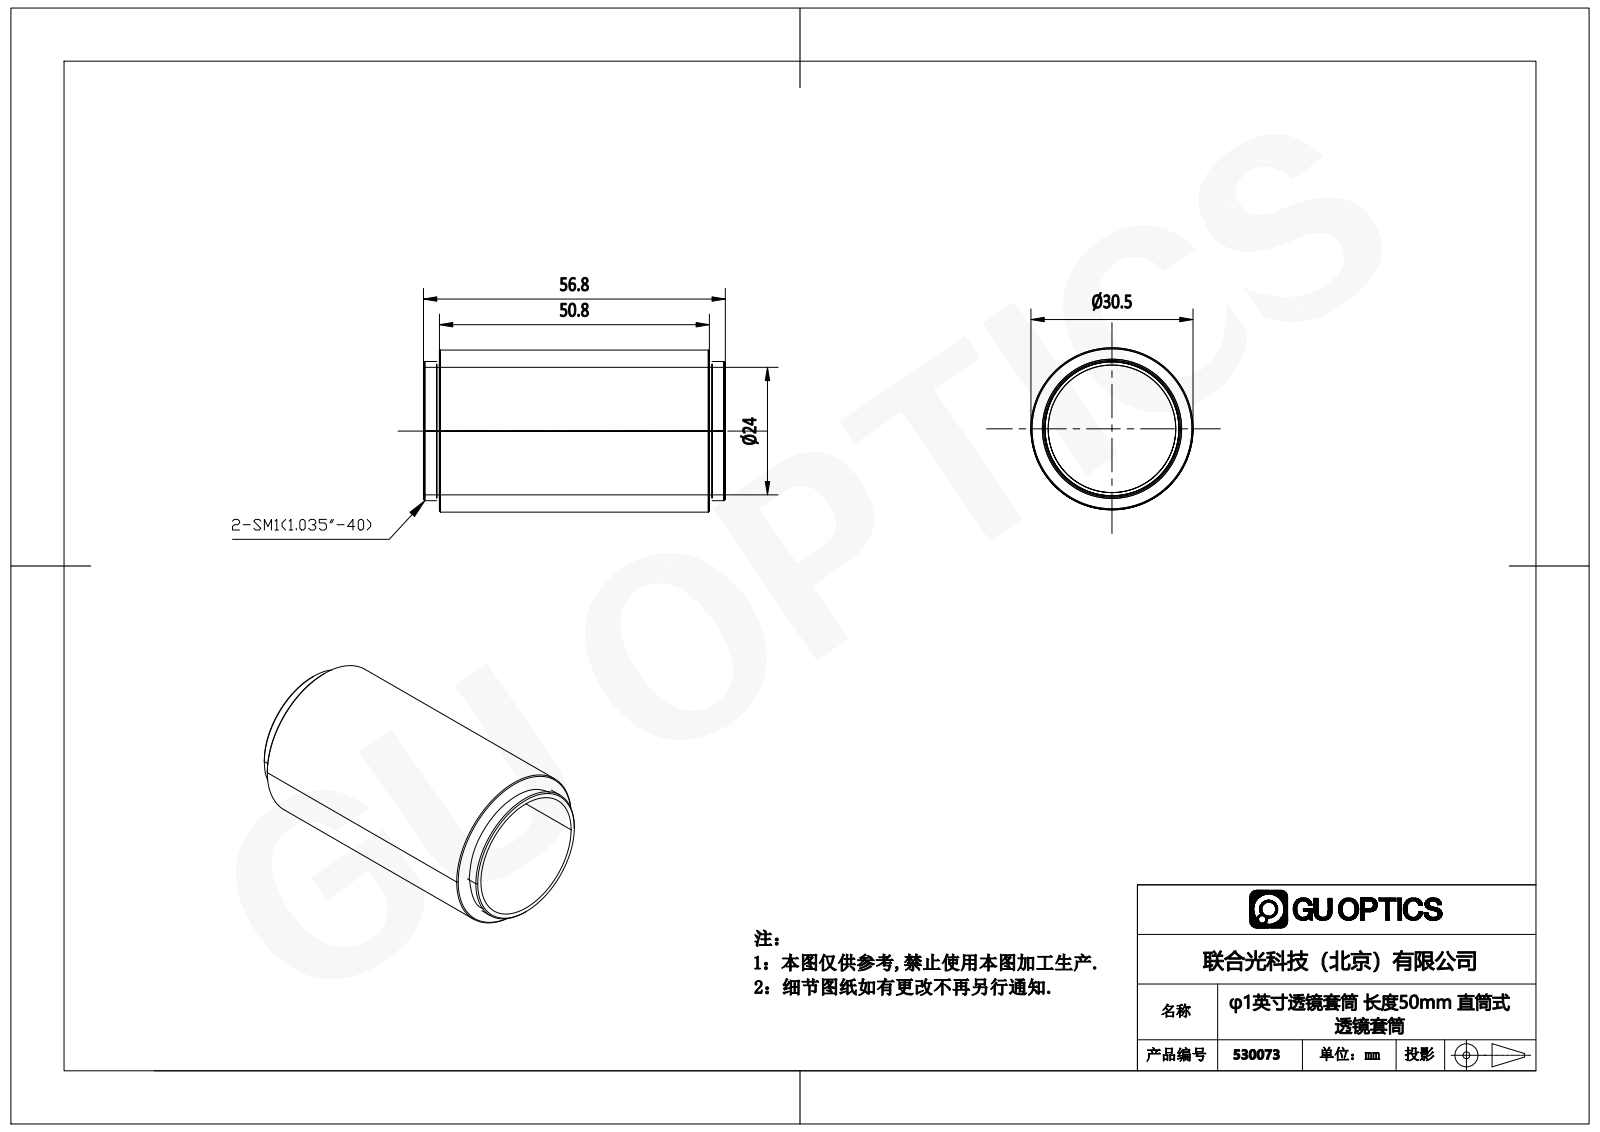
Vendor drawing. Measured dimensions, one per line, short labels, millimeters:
written by: SolidWorks 2018 (AUTOMOTIVE_DESIGN)
unit: mm
bodies: 0 solids, 24 faces (4 planar, 12 cylindrical, 8 other)
size: 56.8 × 30.5 × 30.5
holes: 1× ⌀24
bosses: 1× ⌀30.5, 1× ⌀26.2, 1× ⌀25.2
face distances: 50.8, 3, 53.8, 56.8
